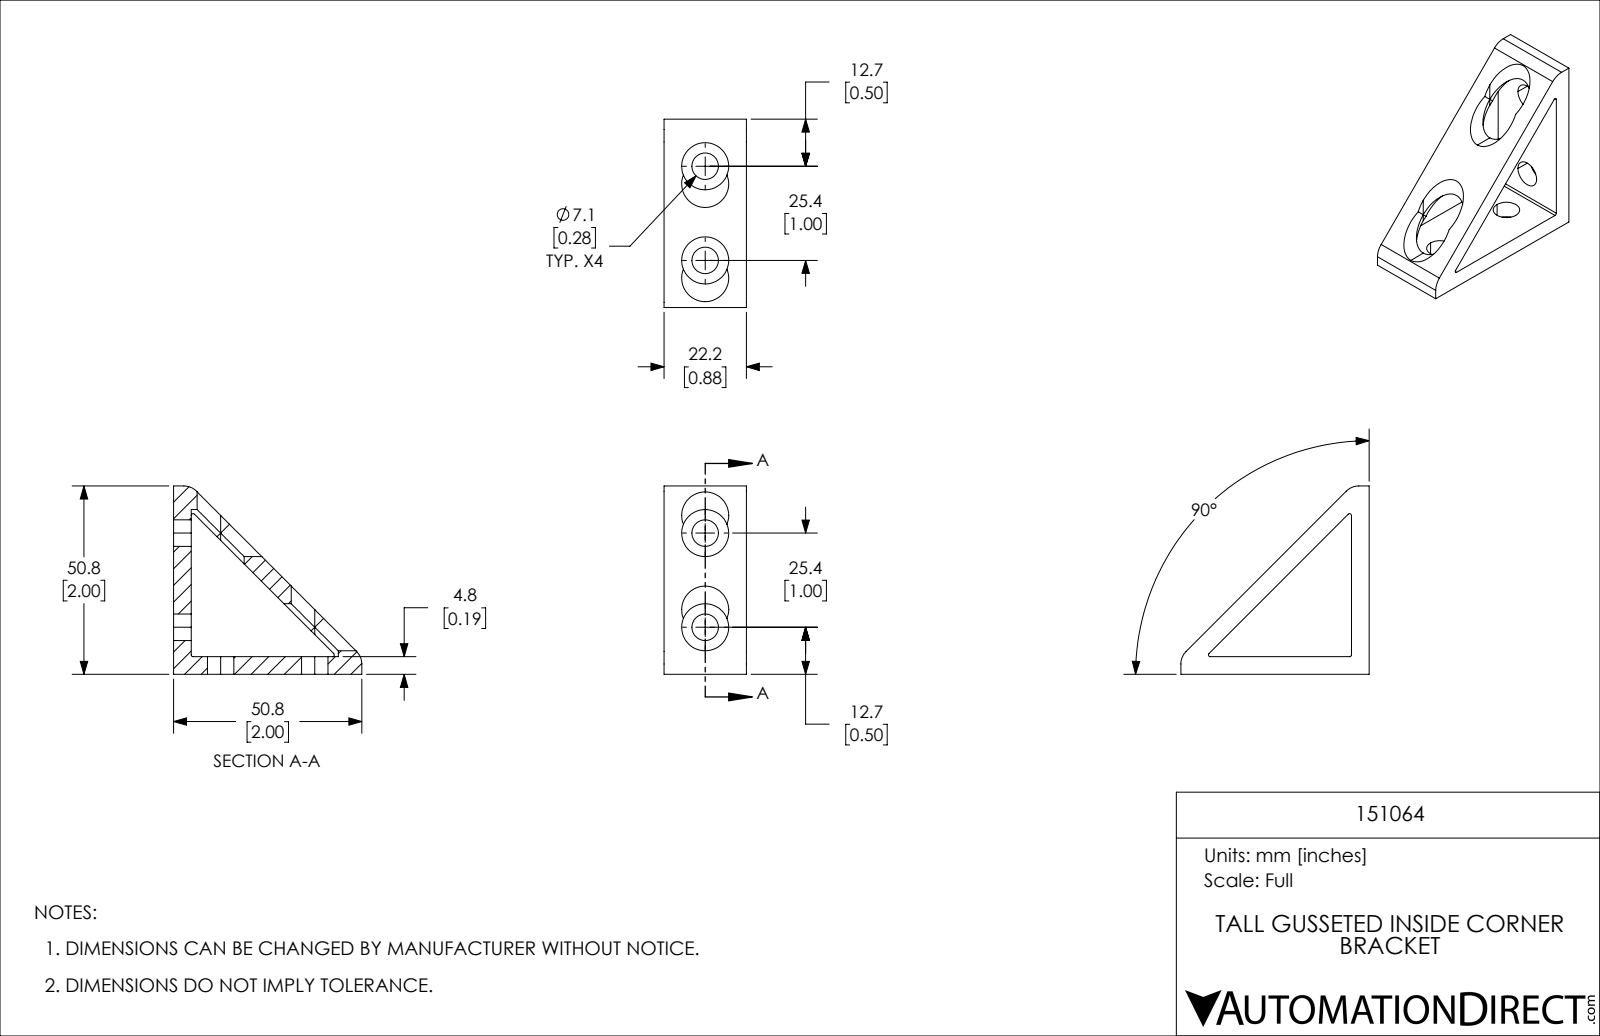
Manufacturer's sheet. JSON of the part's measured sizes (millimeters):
{"part_name": "151064", "step_written_by": "SolidWorks 2021 (CONFIG_CONTROL_DESIGN)", "units": "millimeters", "bodies": {"solids": 1, "faces": 43, "planar": 10, "cylindrical": 33, "other": 0}, "overall_size": [50.8, 50.8, 22.2], "volume_mm3": 13800, "surface_area_mm2": 8090, "round_holes": [[7.1, 4], [12.7, 4]], "partial_cylinders_radius": [[0.5, 3], [4.7, 2]], "face_to_face_distances": [4.7, 22.2, 50.8, 46.1], "hole_center_spacings": [25.4]}
